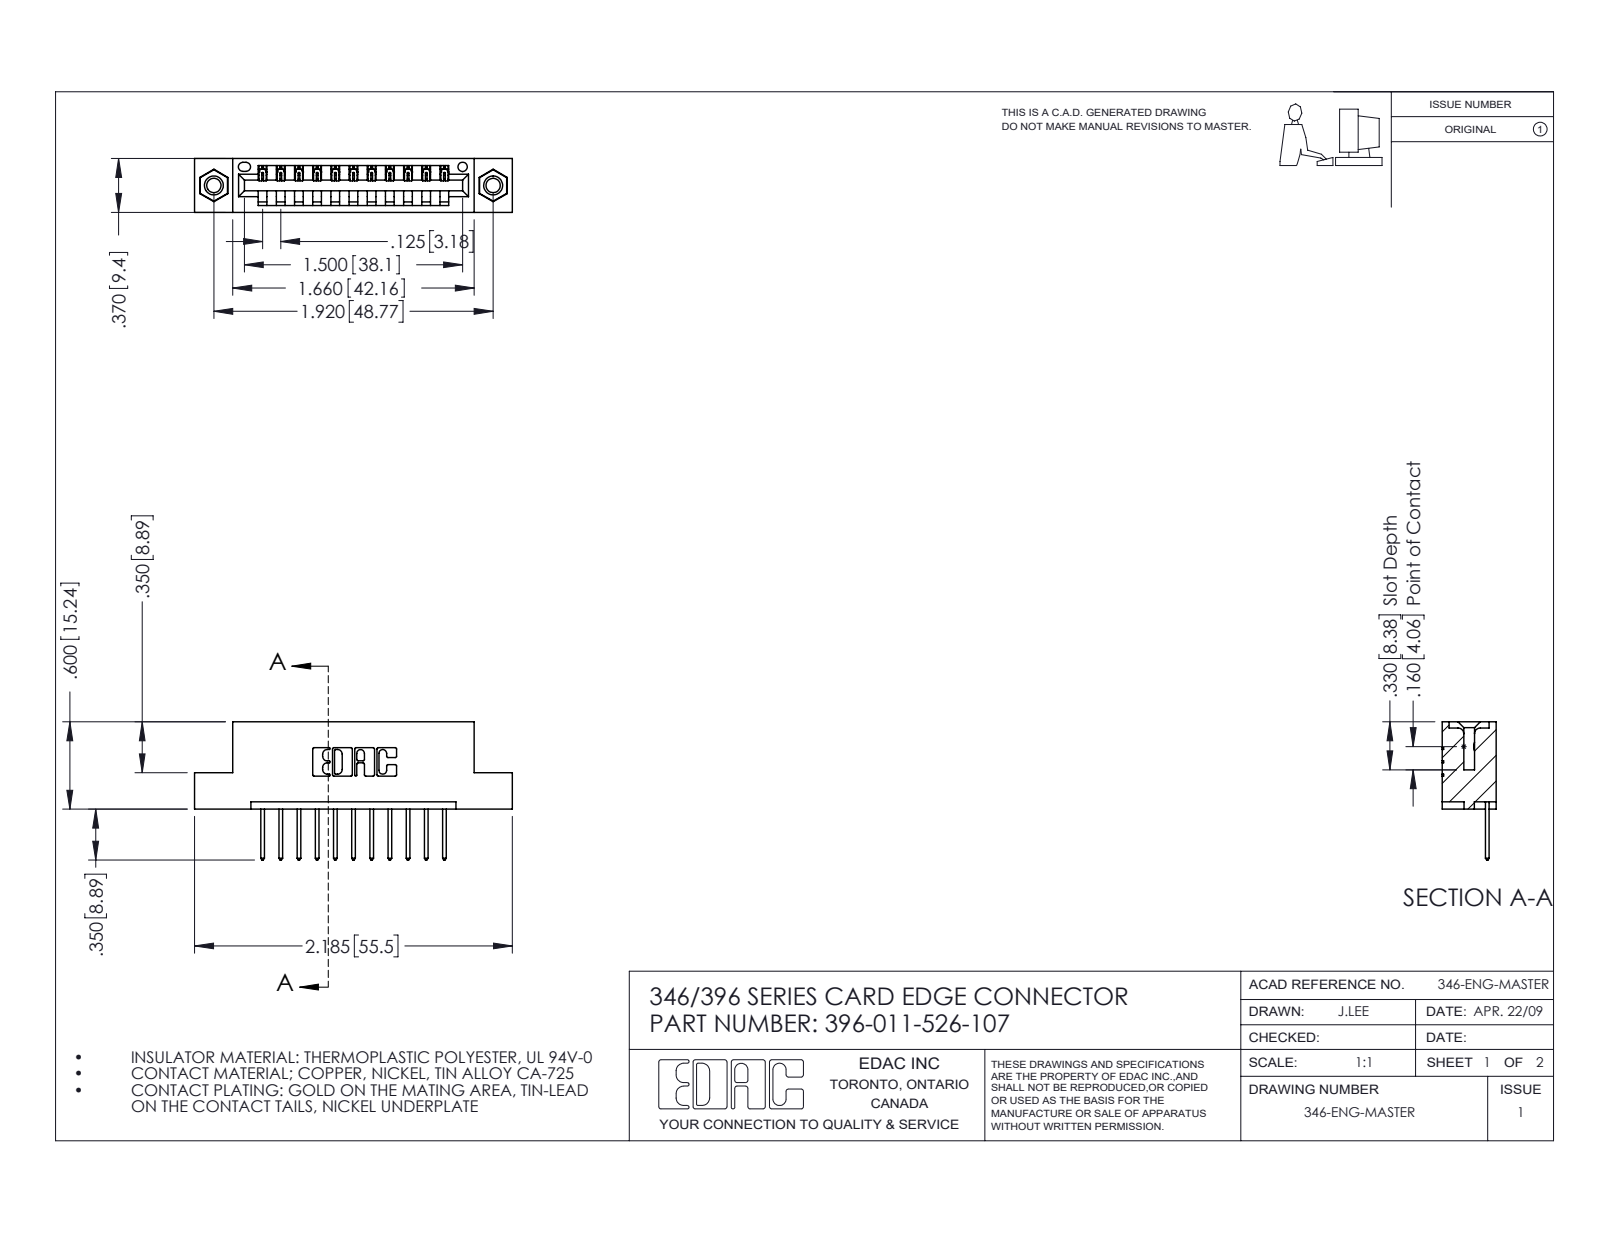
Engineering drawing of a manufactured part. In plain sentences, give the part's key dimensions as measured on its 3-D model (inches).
The part is named "346 Part_Flush Mounting Lugs - 0.156 Dia-TI; 345-250-001_345-250-005-103; 345-292-001_345-293-126; 396-011-526-107". Its 3-D file was written by "SolidWorks 2016 (CONFIG_CONTROL_DESIGN)". It is 14 solids with 820 faces: 548 planar, 256 cylindrical and 16 other. Overall it measures 2.185 by 0.95 by 0.37 inches. Its volume is 0.31 cubic inches and its surface area 9.354 square inches. Round holes: 2 of diameter 0.098, 2 of diameter 0.125, 2 of diameter 0.156, 1 of diameter 0.064. Round bosses or shafts: 2 of diameter 0.155. Partial cylindrical surfaces (rounded edges, fillets, slot ends): 22 of radius 0.006, 22 of radius 0.01, 22 of radius 0.01, 6 of radius 0.007, 6 of radius 0.031, 3 of radius 0.026, 2 of radius 0.031, 2 of radius 0.04. The main face-to-face distances are 0.25, 0.048, 0.322, 0.37, 0.072, 0.298, 0.025, 0.148, 0.222, 0.1. The hole center spacings are 0.246, 1.715, 1.92.
